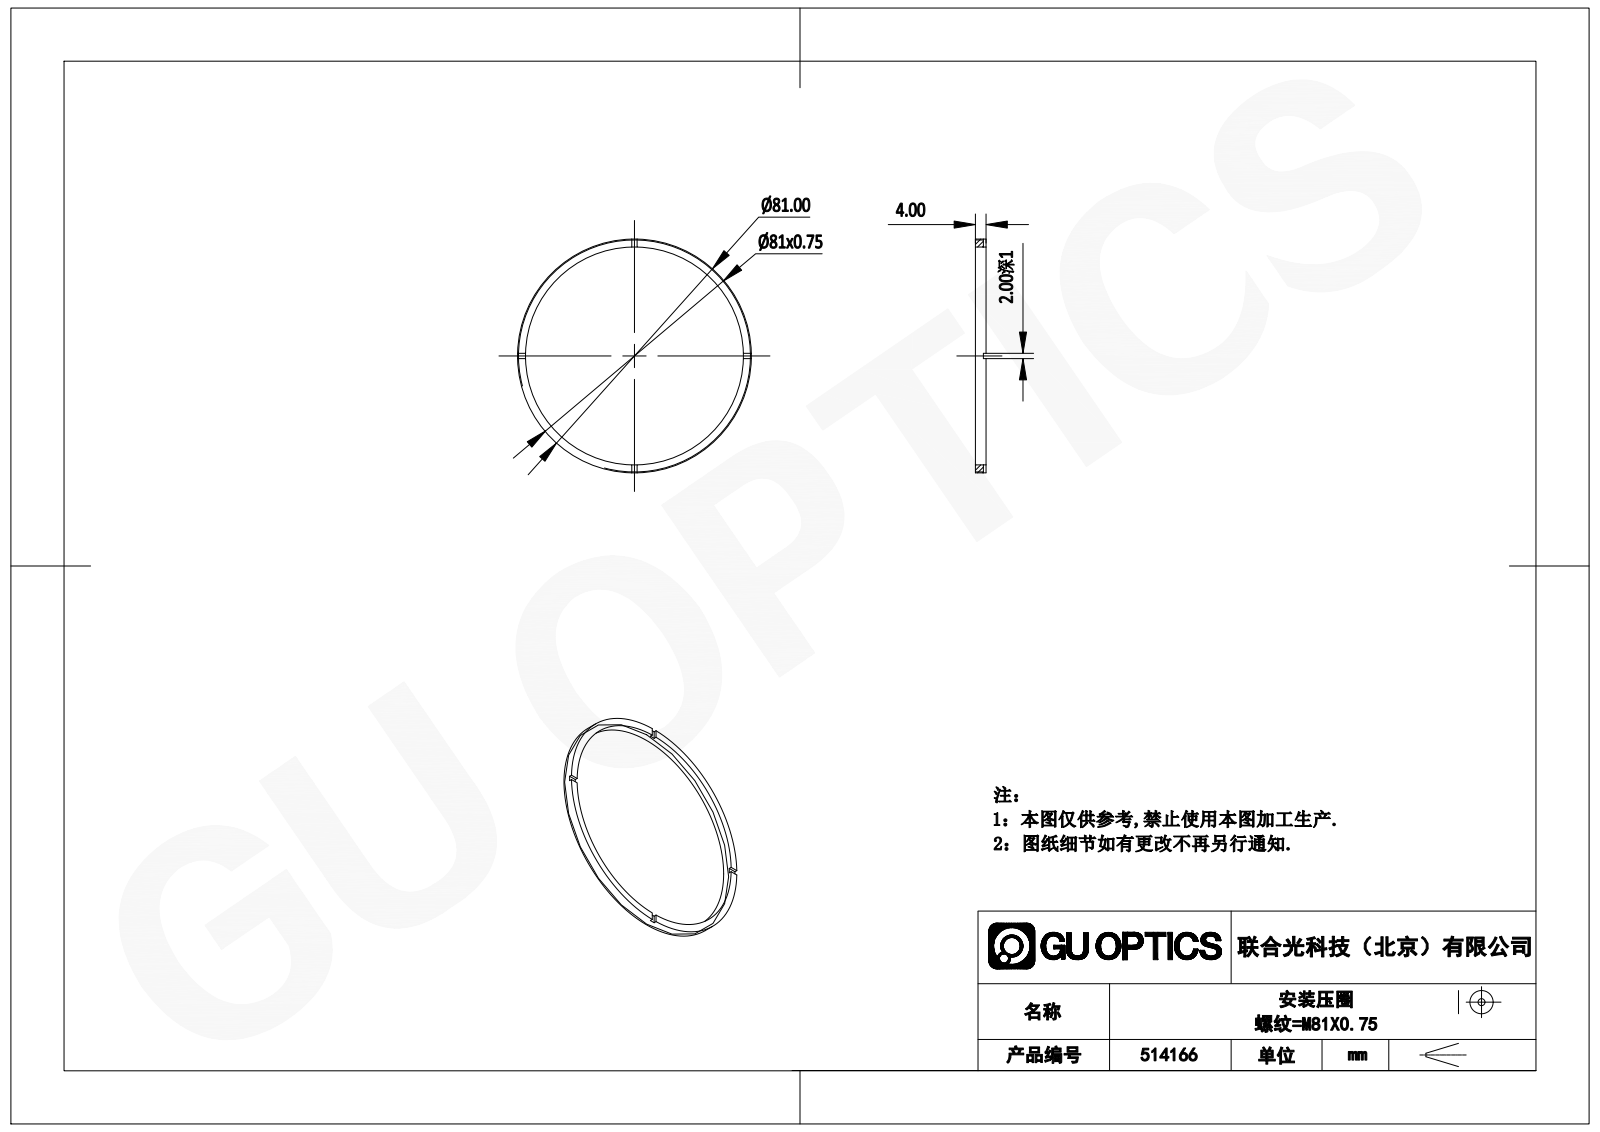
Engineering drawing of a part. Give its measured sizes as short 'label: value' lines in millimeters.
name: 514166
written by: SolidWorks 2020 (CONFIG_CONTROL_DESIGN)
unit: mm
bodies: 1 solid, 21 faces (17 planar, 4 cylindrical, 0 other)
size: 81 × 81 × 4
volume: 2 917 mm³; area: 3 439 mm²
holes: 1× ⌀75
bosses: 1× ⌀81
face distances: 4, 3, 1, 2
